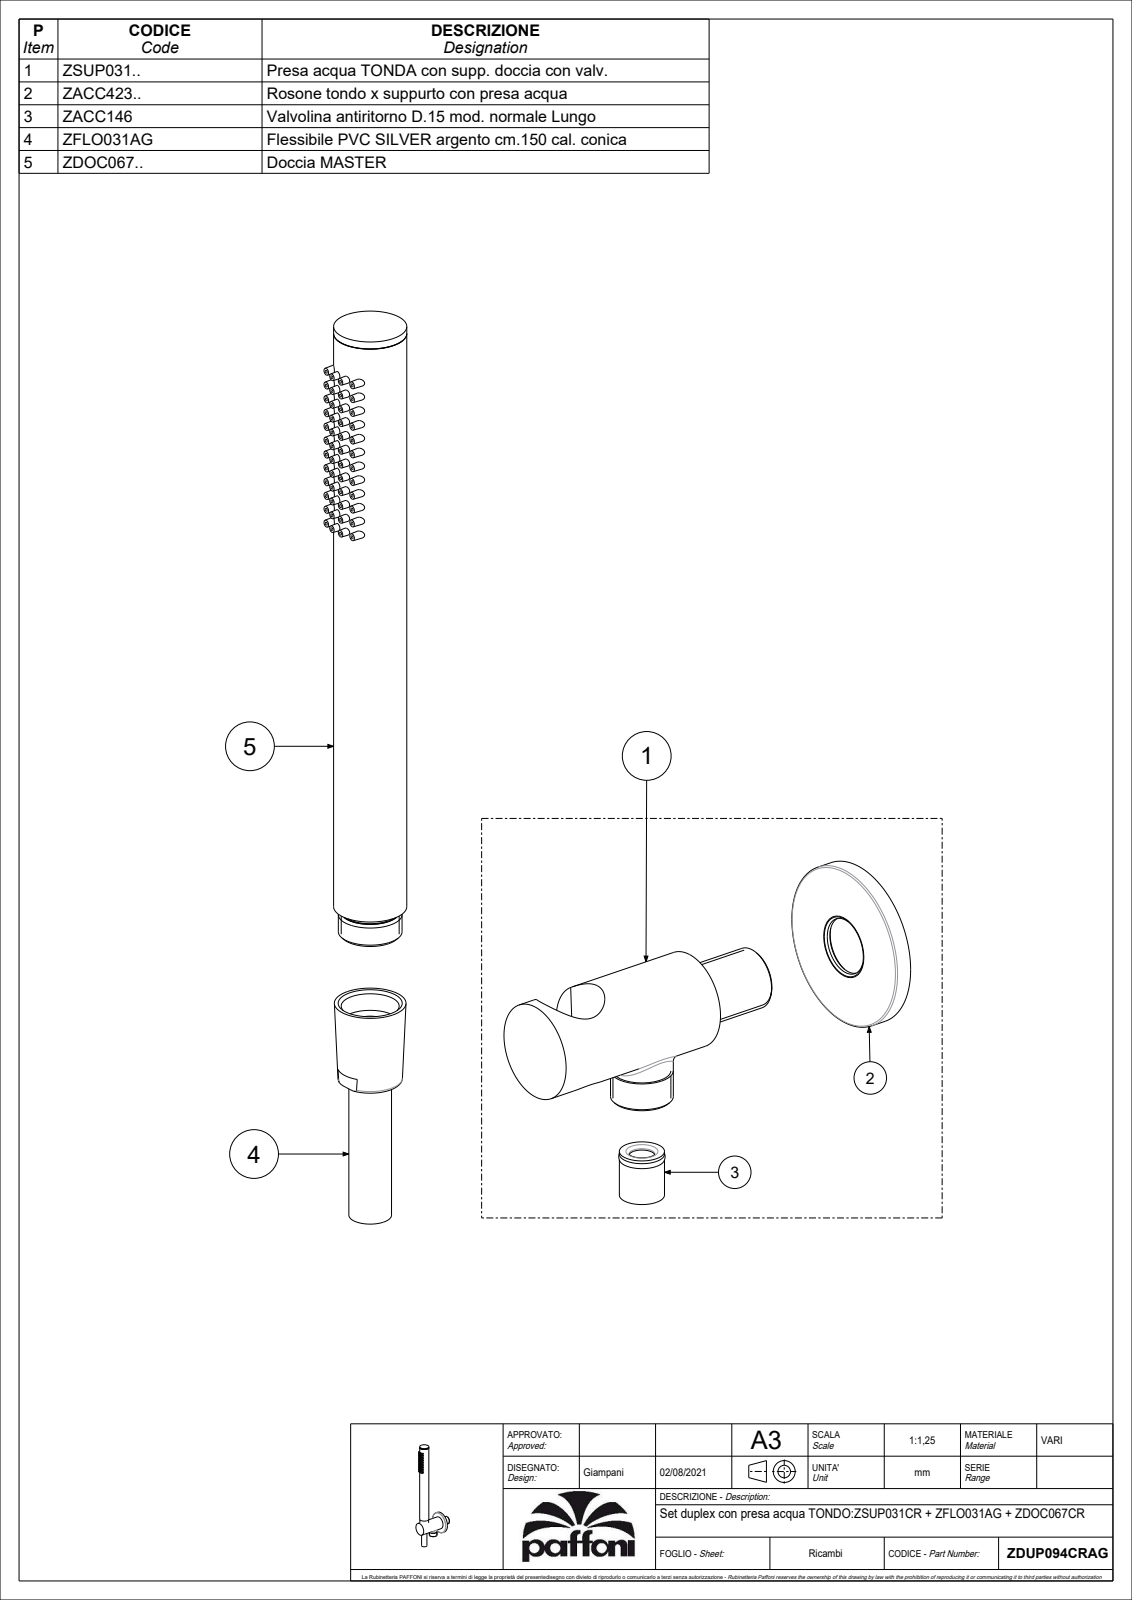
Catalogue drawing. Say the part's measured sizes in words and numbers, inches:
The part is named "ZDUP094CRAG". Its 3-D file was written by "CREO PARAMETRIC BY PTC INC, 2020044 (CONFIG_CONTROL_DESIGN)". It is 21 solids with 458 faces: 154 planar, 171 cylindrical and 133 other. Overall it measures 10.894 by 2.795 by 2.165 inches. Its volume is 4.257 cubic inches and its surface area 88.98 square inches. Round holes: 50 of diameter 0.039, 2 of diameter 0.591, 2 of diameter 0.748, 1 of diameter 0.394, 1 of diameter 0.512, 1 of diameter 0.571, 1 of diameter 0.787, 1 of diameter 1.102, 1 of diameter 2.067. Round bosses or shafts: 2 of diameter 0.811, 1 of diameter 2.165, 1 of diameter 1.28, 1 of diameter 1.043, 1 of diameter 0.945, 1 of diameter 0.827, 1 of diameter 0.787, 1 of diameter 0.728. Partial cylindrical surfaces (rounded edges, fillets, slot ends): 1 of radius 0.222. The main face-to-face distances are 0.059, 2.559, 2.618, 1.476, 0.177, 0.197, 1.535, 1.083, 0.236, 0.039. The hole center spacings are 0.252, 0.424, 0.611, 0.197, 0.394, 0.803, 0.591, 0.157.
